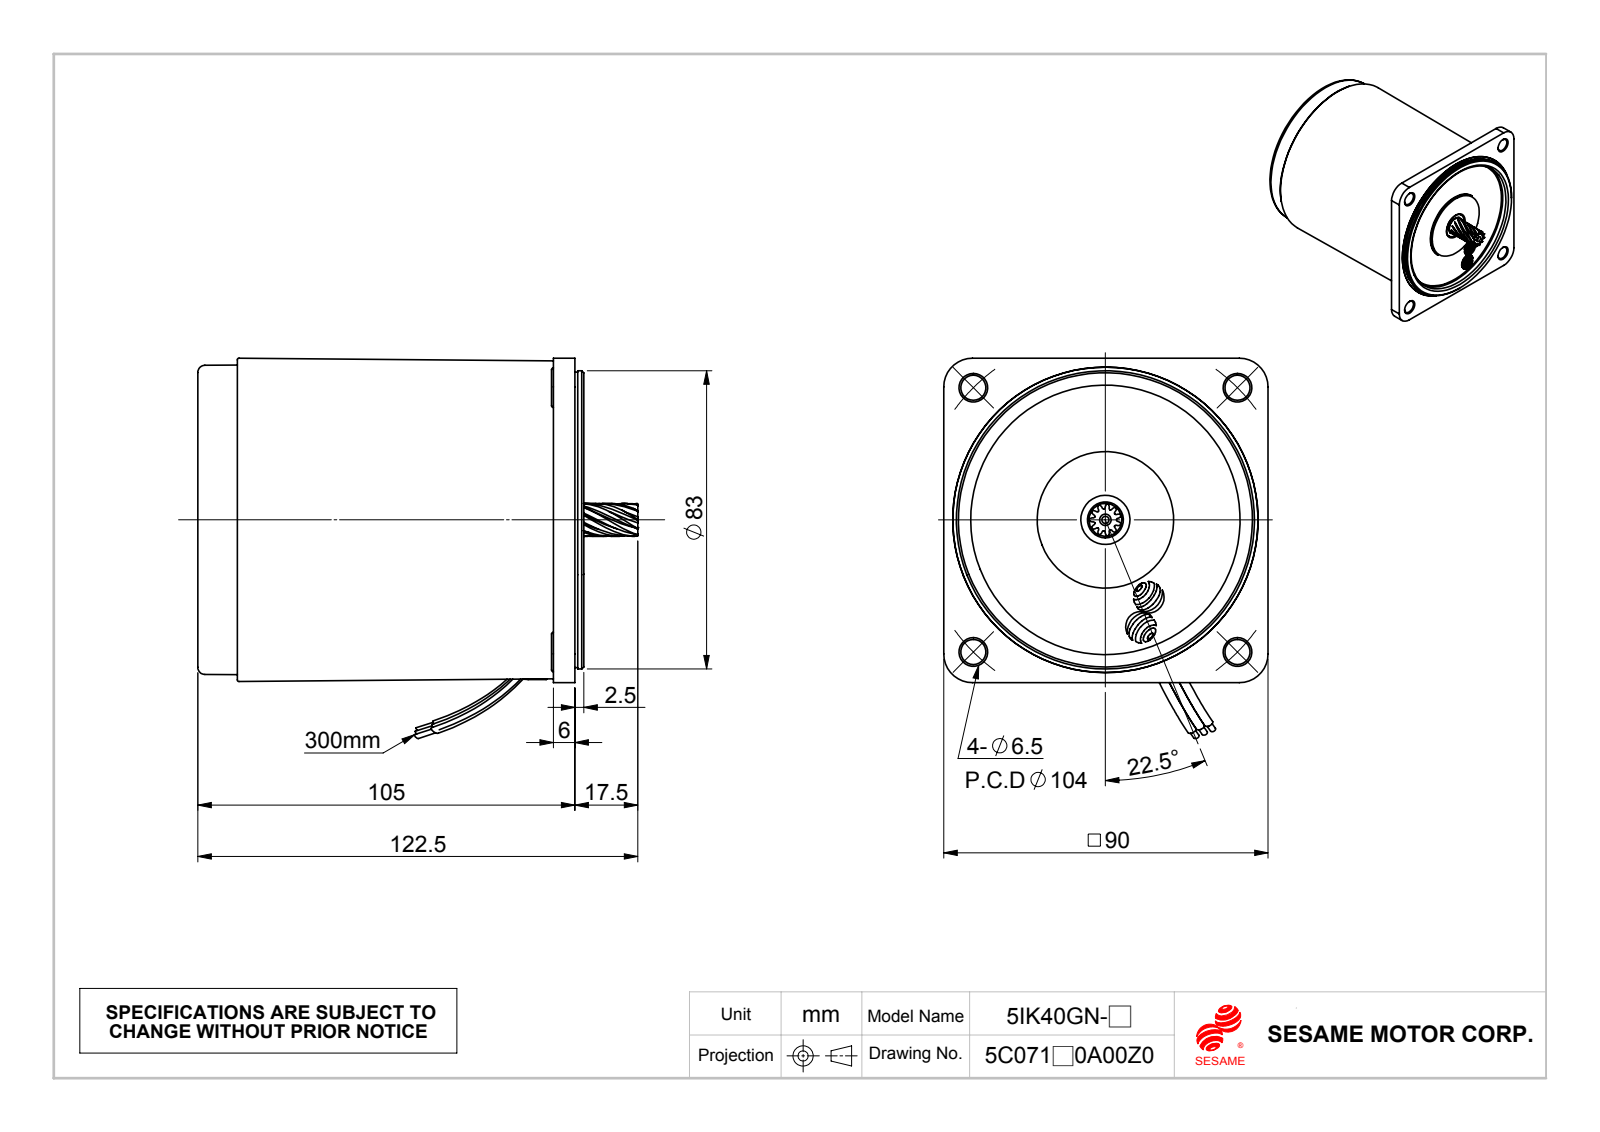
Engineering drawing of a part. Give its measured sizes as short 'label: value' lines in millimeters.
name: 線扣; M540; 40GN
written by: SolidWorks 2010 (CONFIG_CONTROL_DESIGN)
unit: mm
bodies: 7 solids, 402 faces (73 planar, 203 cylindrical, 126 other)
size: 122.5 × 105.88 × 90.3
volume: 662 518 mm³; area: 65 518 mm²
holes: 4× ⌀7, 1× ⌀2, 1× ⌀2.5, 1× ⌀7.2, 1× ⌀9.5, 1× ⌀13.7, 1× ⌀26, 1× ⌀58.1, 1× ⌀75, 1× ⌀84.4, 1× ⌀85
bosses: 1× ⌀84.22, 1× ⌀84.15, 1× ⌀83, 1× ⌀82.2, 1× ⌀38, 1× ⌀10, 1× ⌀9.3, 1× ⌀9.17
rounds: 8× R0.25, 8× R0.78, 8× R1.5, 8× R1.66, 8× R2.92, 4× R0.2, 4× R0.58, 4× R2.58
face distances: 1, 102.5, 0.9, 103.5, 2.5, 101.5, 102.4, 103.4, 1.5, 104
hole spacings: 52, 73.54, 104
